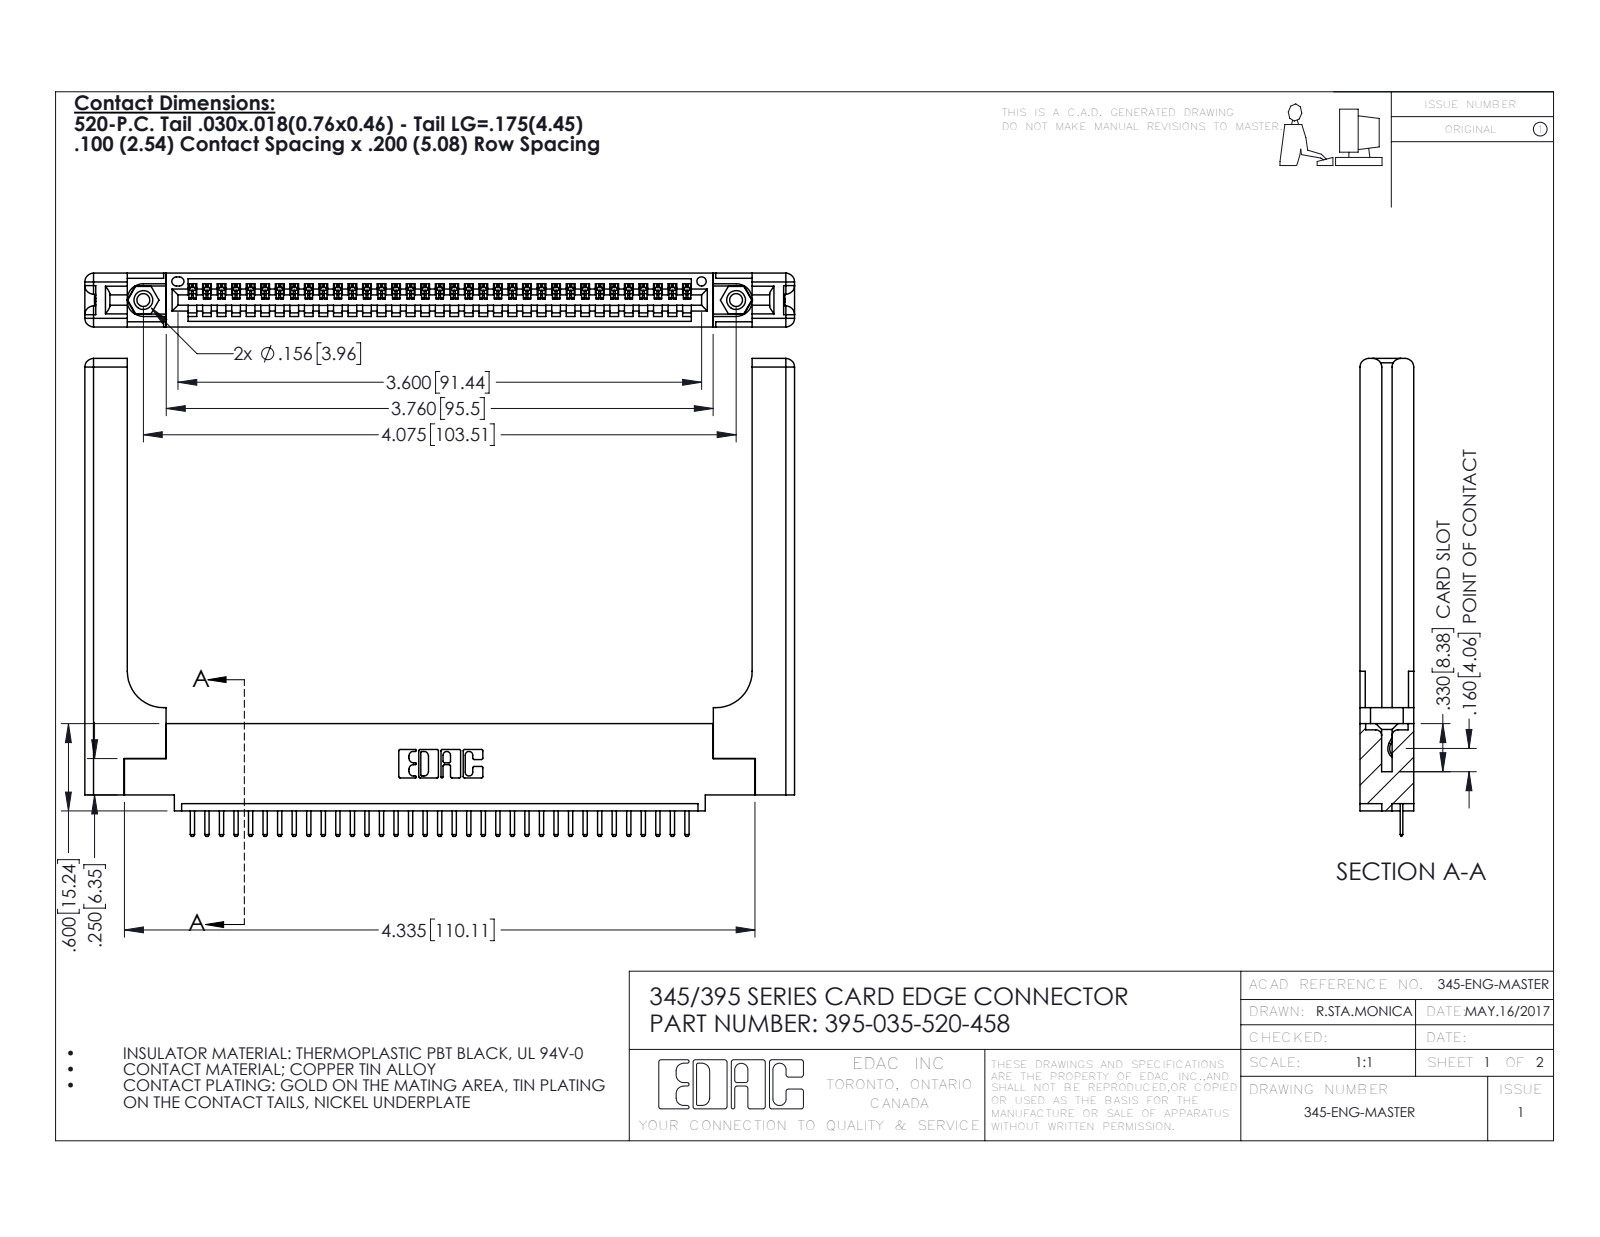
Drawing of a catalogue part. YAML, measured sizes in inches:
part_name: "345 Part_0.110 Offset - 0.156 Dia-TH; 345-220-058_345-220-058; 345-250-001_345-250-001-102; 395-035-520-458 (+1 more)"
step_written_by: "SolidWorks 2016 (CONFIG_CONTROL_DESIGN)"
units: inches
bodies: {solids: 40, faces: 2556, planar: 1702, cylindrical: 794, other: 60}
overall_size: [4.879, 3.285, 0.37]
volume: 1.223
surface_area: 31.46
round_holes:
  - {diameter: 0.089, count: 2}
  - {diameter: 0.125, count: 2}
  - {diameter: 0.156, count: 2}
  - {diameter: 0.064, count: 1}
round_bosses_or_shafts:
  - {diameter: 0.155, count: 2}
partial_cylinders:
  - {radius: 0.01, count: 72}
  - {radius: 0.006, count: 70}
  - {radius: 0.01, count: 22}
  - {radius: 0.06, count: 16}
  - {radius: 0.007, count: 6}
  - {radius: 0.031, count: 6}
  - {radius: 0.026, count: 3}
  - {radius: 0.03, count: 2}
face_to_face_distances: [0.37, 0.072, 0.298, 0.098, 0.272, 0.025, 0.2, 0.148, 0.15, 0.225]
hole_center_spacings: [0.27, 3.839, 4.075]
